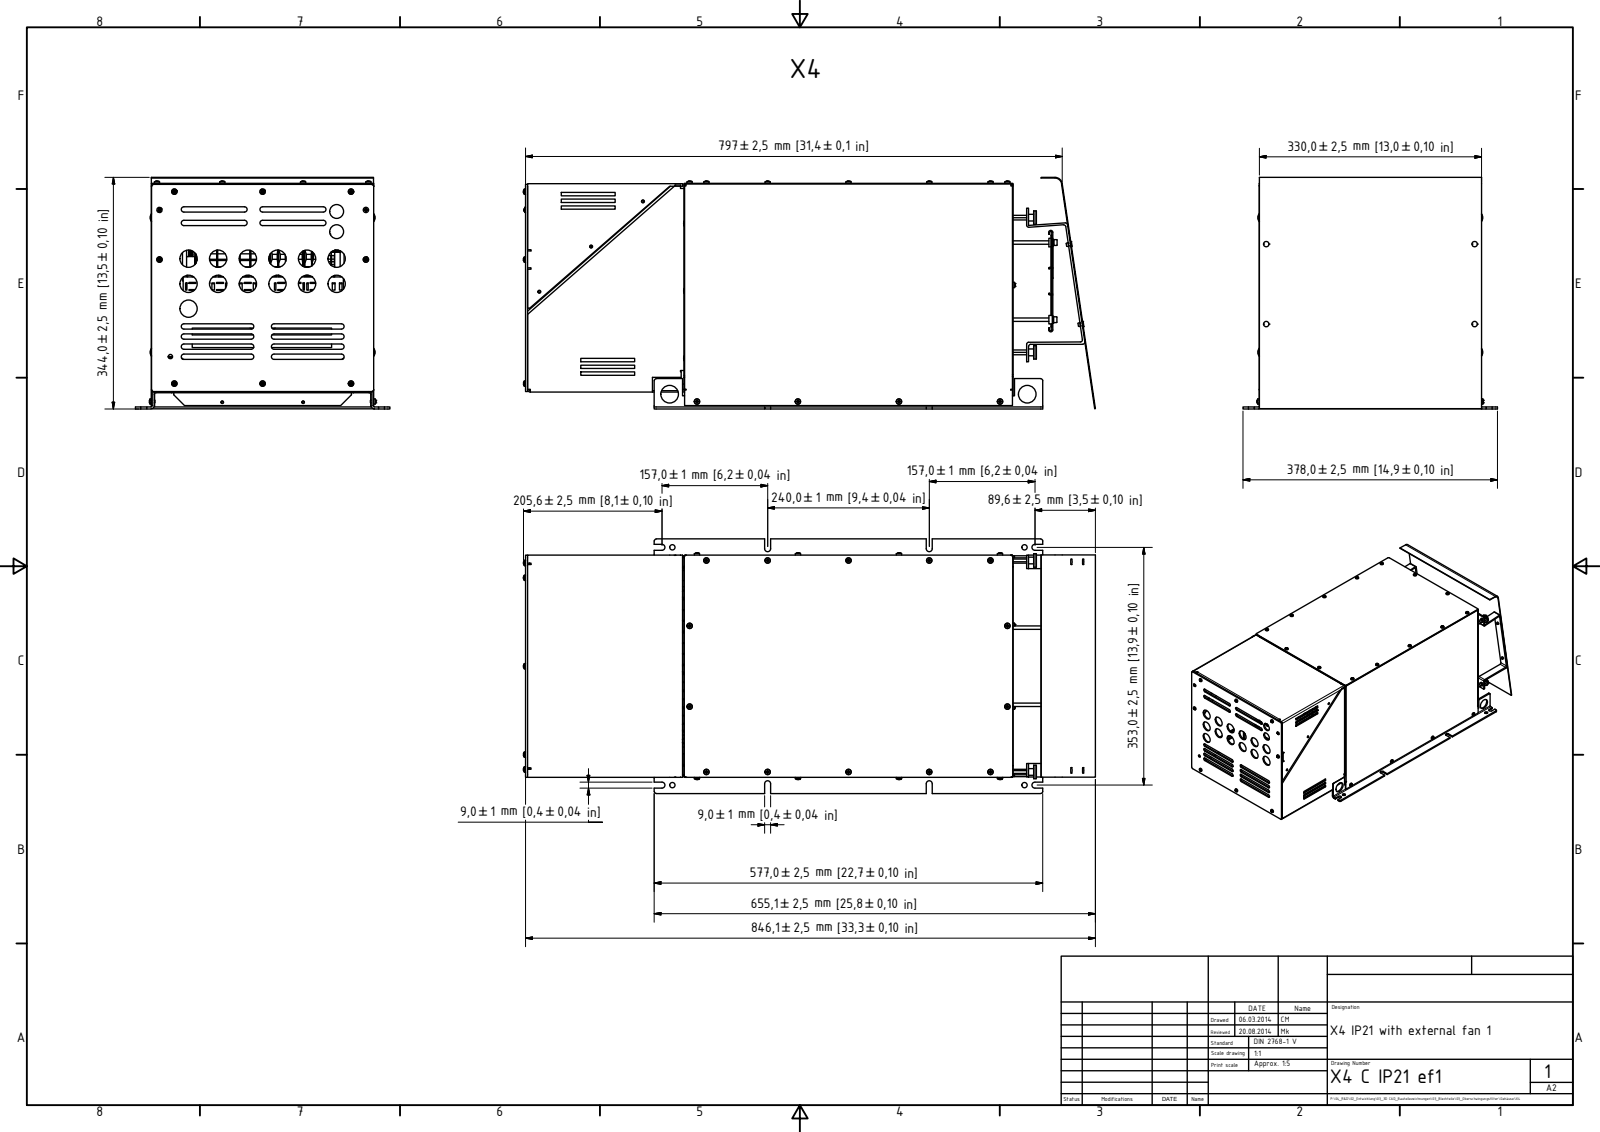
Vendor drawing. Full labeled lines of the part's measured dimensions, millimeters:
Part name (STEP PRODUCT): 10100257 Bodenblech X4; 10100395 Seitenwand RHF-BG X4-A; 10100394 Lüfterblech RHF-BG X4-A; 10100393 Deckel RHF-BG X4-A (+8 more)
STEP written by: Autodesk Inventor 2015 (AUTOMOTIVE_DESIGN)
Units: millimetres
Bodies: 138 solids, 9673 faces (5806 planar, 2804 cylindrical, 1063 other)
Overall size (bounding box): 849.25 × 378 × 343.93
Volume: 2 948 000 mm³ · Surface area: 3 408 000 mm²
Round holes (diameter × count): ⌀3.24 ×46, ⌀5 ×38, ⌀6.8 ×19, ⌀4 ×13, ⌀25.5 ×13, ⌀8.25 ×12, ⌀8 ×10, ⌀7 ×6, ⌀11 ×6, ⌀6 ×5, ⌀6.5 ×5, ⌀4.13 ×4
Round bosses / shafts (diameter × count): ⌀4 ×45, ⌀3.65 ×38, ⌀1.4 ×8, ⌀10 ×6, ⌀8 ×6, ⌀8.5 ×5, ⌀20 ×4, ⌀16 ×4
Partial cylindrical surfaces — rounded edges, fillets, slot ends (radius × count): R0.5 ×109, R0.72 ×104, R0.1 ×61, R1 ×60, R0.15 ×58, R2 ×51, R0.1 ×41, R3 ×39
Main face-to-face distances: 1, 2, 329, 328, 3, 330, 308, 310, 307, 488
Hole centre spacings: 120, 21, 309.5, 314, 36.37, 27, 46, 0.48
